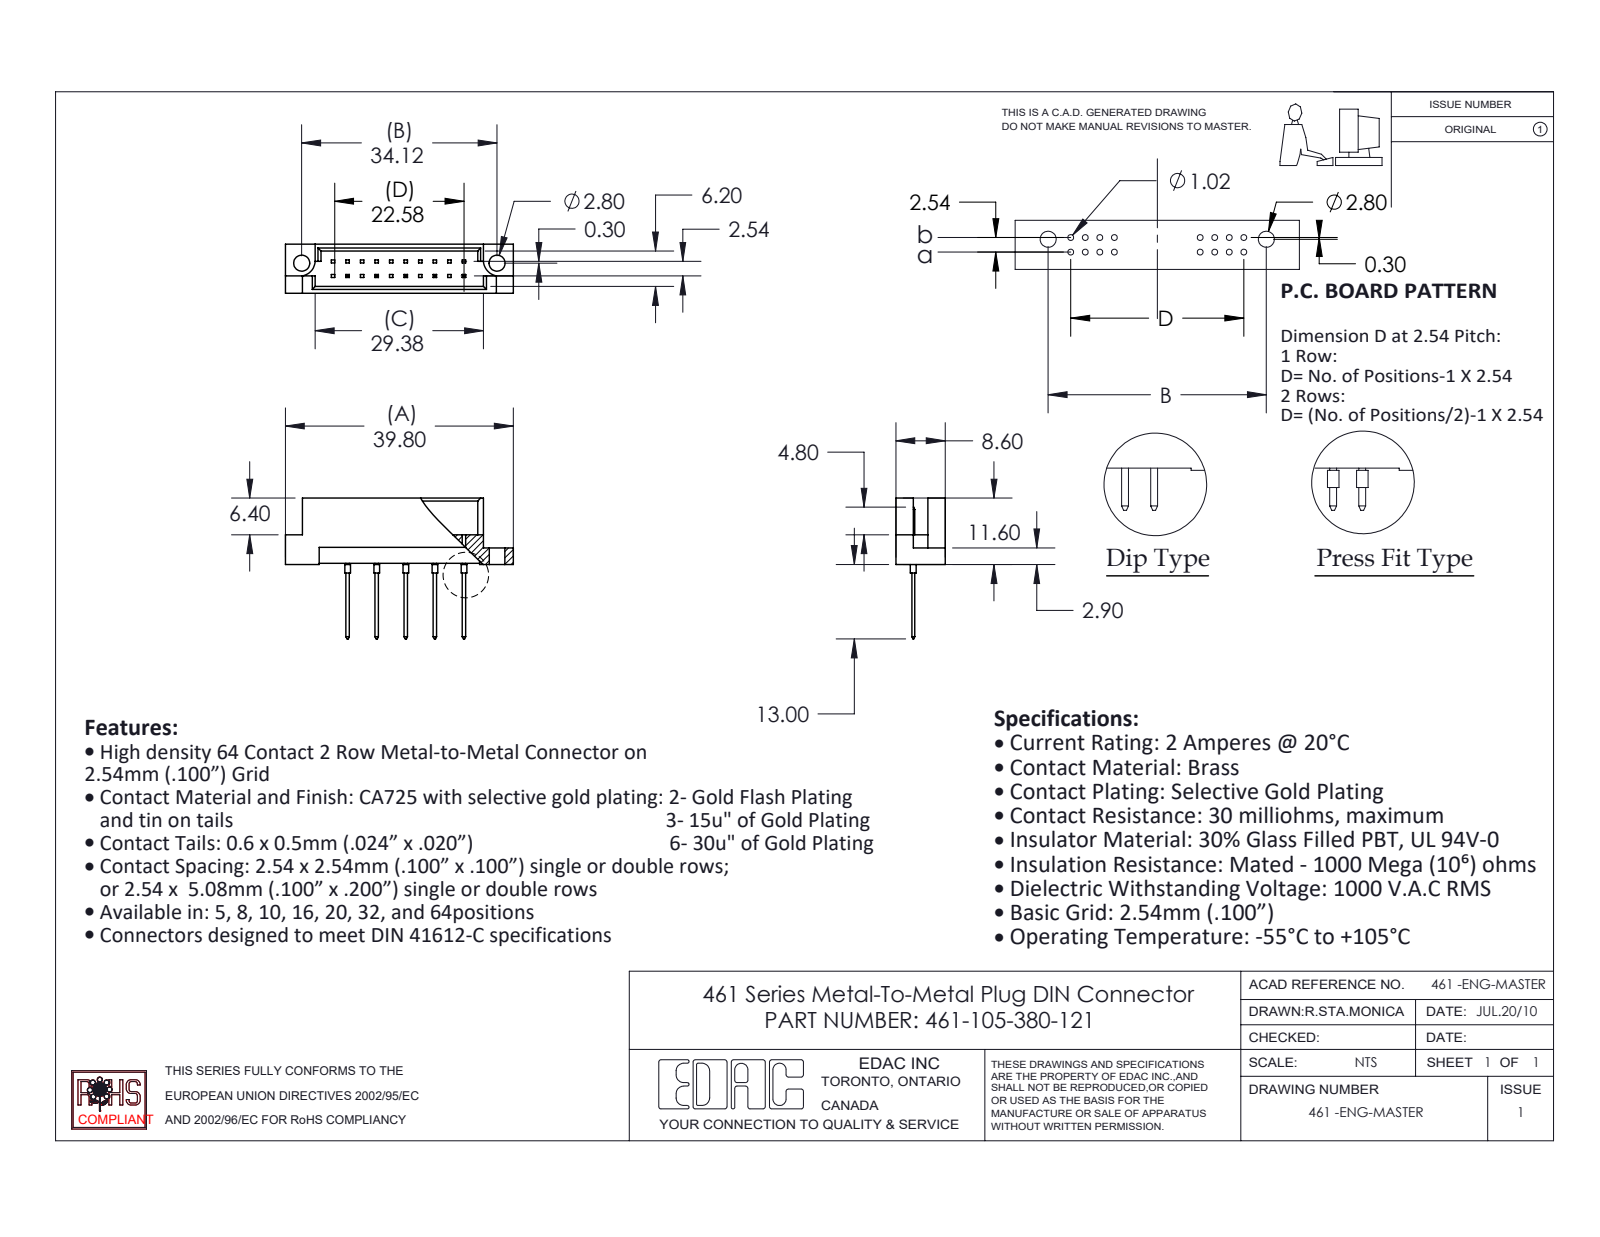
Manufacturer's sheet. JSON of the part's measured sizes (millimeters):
{"part_name": "461-105-380-121; 461-290_80; 461 Part_20", "step_written_by": "SolidWorks 2020 (CONFIG_CONTROL_DESIGN)", "units": "millimeters", "bodies": {"solids": 6, "faces": 238, "planar": 222, "cylindrical": 16, "other": 0}, "overall_size": [39.8, 24.6, 8.6], "volume_mm3": 1942, "surface_area_mm2": 2601, "round_holes": [[2.8, 2]], "round_bosses_or_shafts": [[1, 5]], "partial_cylinders_radius": [[2.8, 2]], "face_to_face_distances": [1.2, 7.4, 8.6, 6.2, 5, 5.08, 3.28, 5.32, 2.08, 4.12], "hole_center_spacings": [34.12]}
